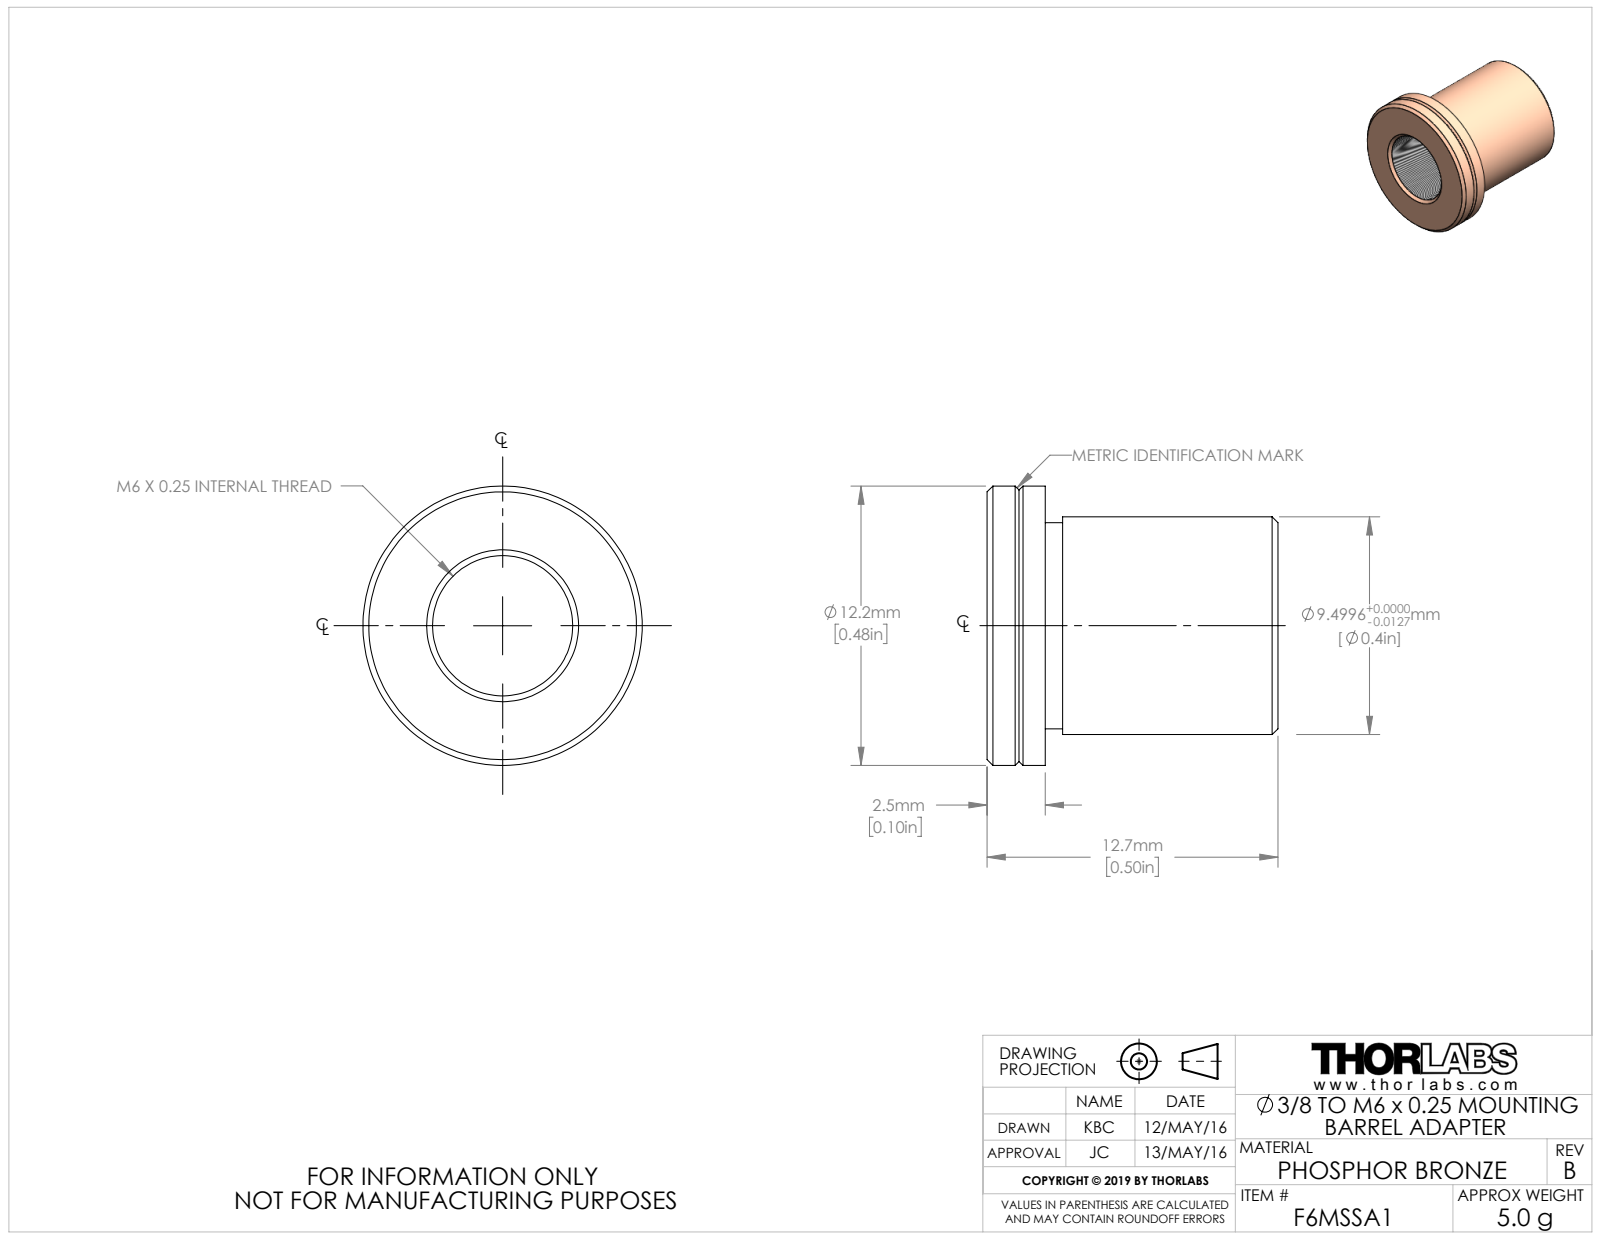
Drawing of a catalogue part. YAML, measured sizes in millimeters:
part_name: "TTN102536-E0W"
step_written_by: "SolidWorks 2016 (CONFIG_CONTROL_DESIGN)"
units: millimeters
bodies: {solids: 1, faces: 26, planar: 4, cylindrical: 10, other: 12}
overall_size: [12.7, 12.19, 12.19]
volume: 633
surface_area: 822
round_holes:
  - {diameter: 6.12, count: 1}
round_bosses_or_shafts:
  - {diameter: 12.19, count: 1}
  - {diameter: 9.5, count: 1}
  - {diameter: 8.99, count: 1}
face_to_face_distances: [2.54, 10.16, 12.7, 9.4, 0.76, 3.3]
